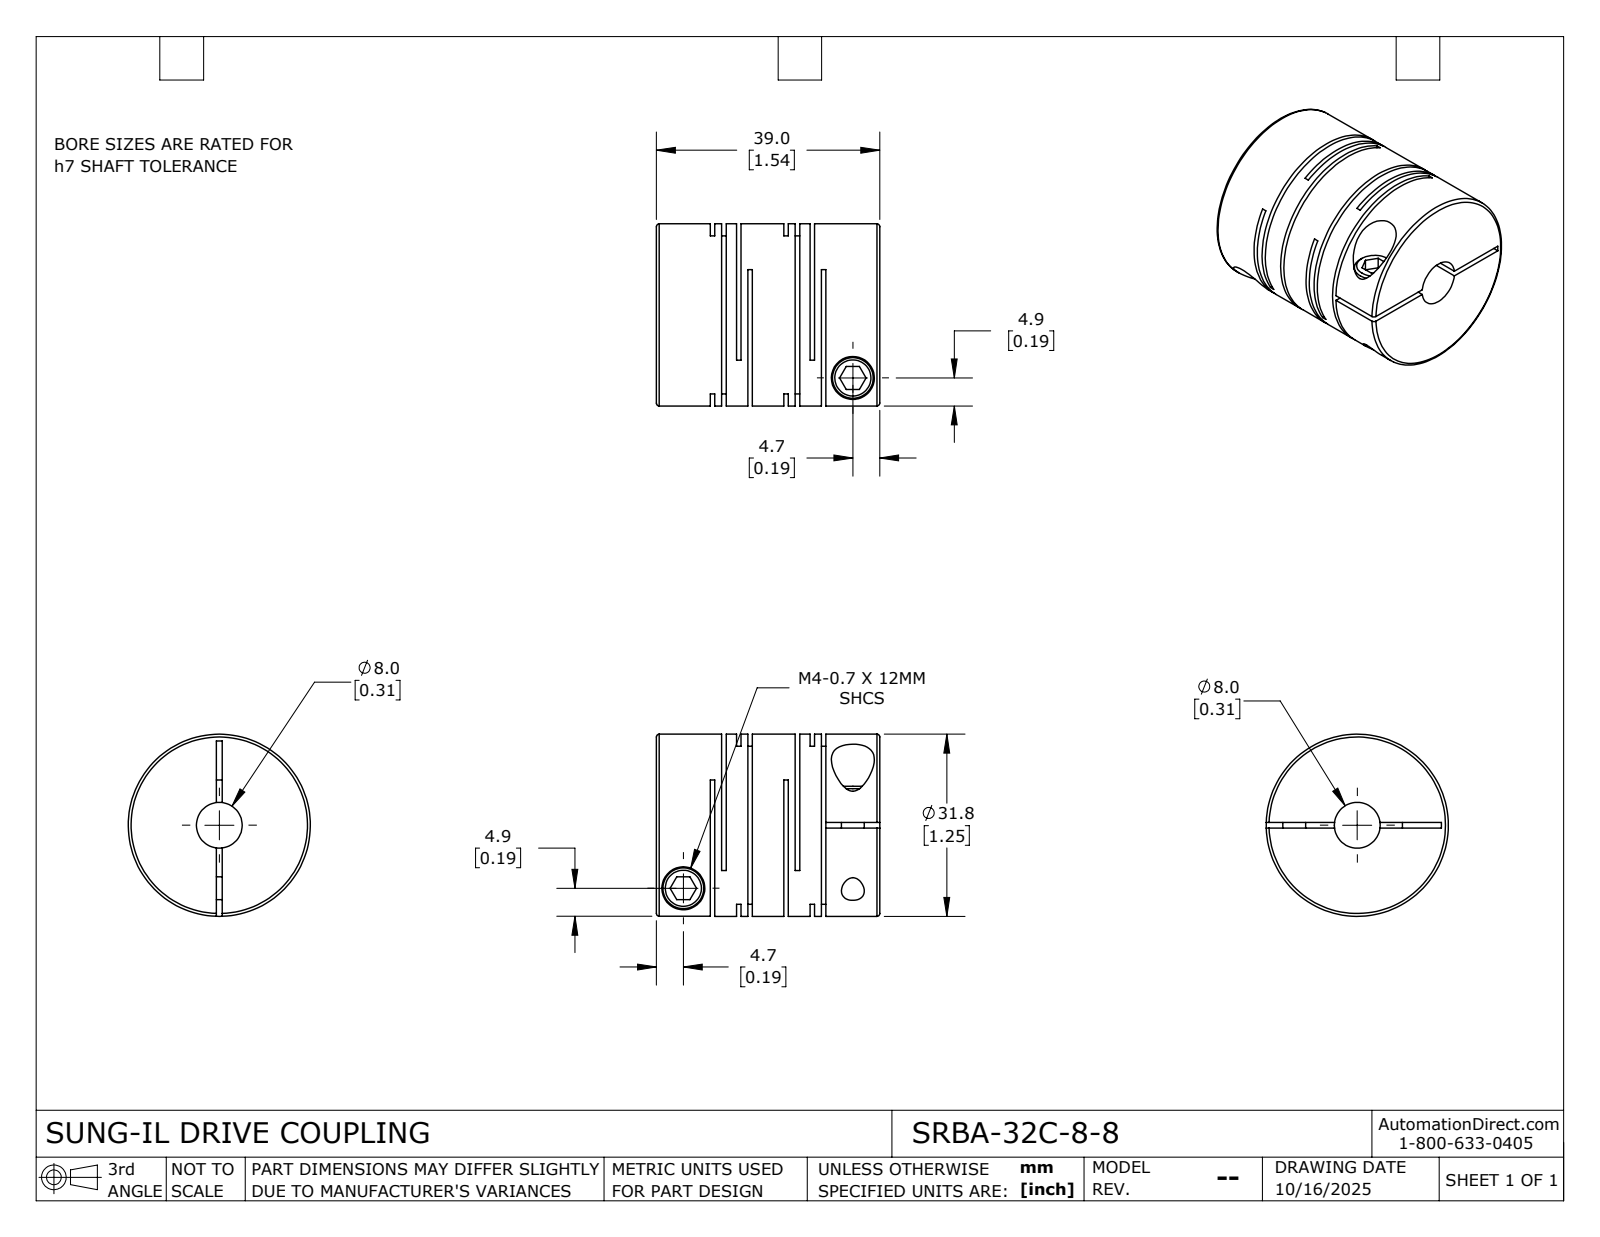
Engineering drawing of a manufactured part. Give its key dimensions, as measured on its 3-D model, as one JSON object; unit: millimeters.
{"part_name": "SRBA-32C-8-8", "step_written_by": "SolidWorks 2024 (CONFIG_CONTROL_DESIGN)", "units": "millimeters", "bodies": {"solids": 1, "faces": 115, "planar": 60, "cylindrical": 42, "other": 13}, "overall_size": [39, 31.8, 31.8], "volume_mm3": 24313, "surface_area_mm2": 16577, "round_holes": [[4, 2], [7.5, 2], [8, 1]], "round_bosses_or_shafts": [[7.1, 2], [31.8, 1]], "face_to_face_distances": [12.84, 0.8, 1.98, 4.58, 12.04, 1.18, 10.86, 3.78, 8.26, 2.6]}
